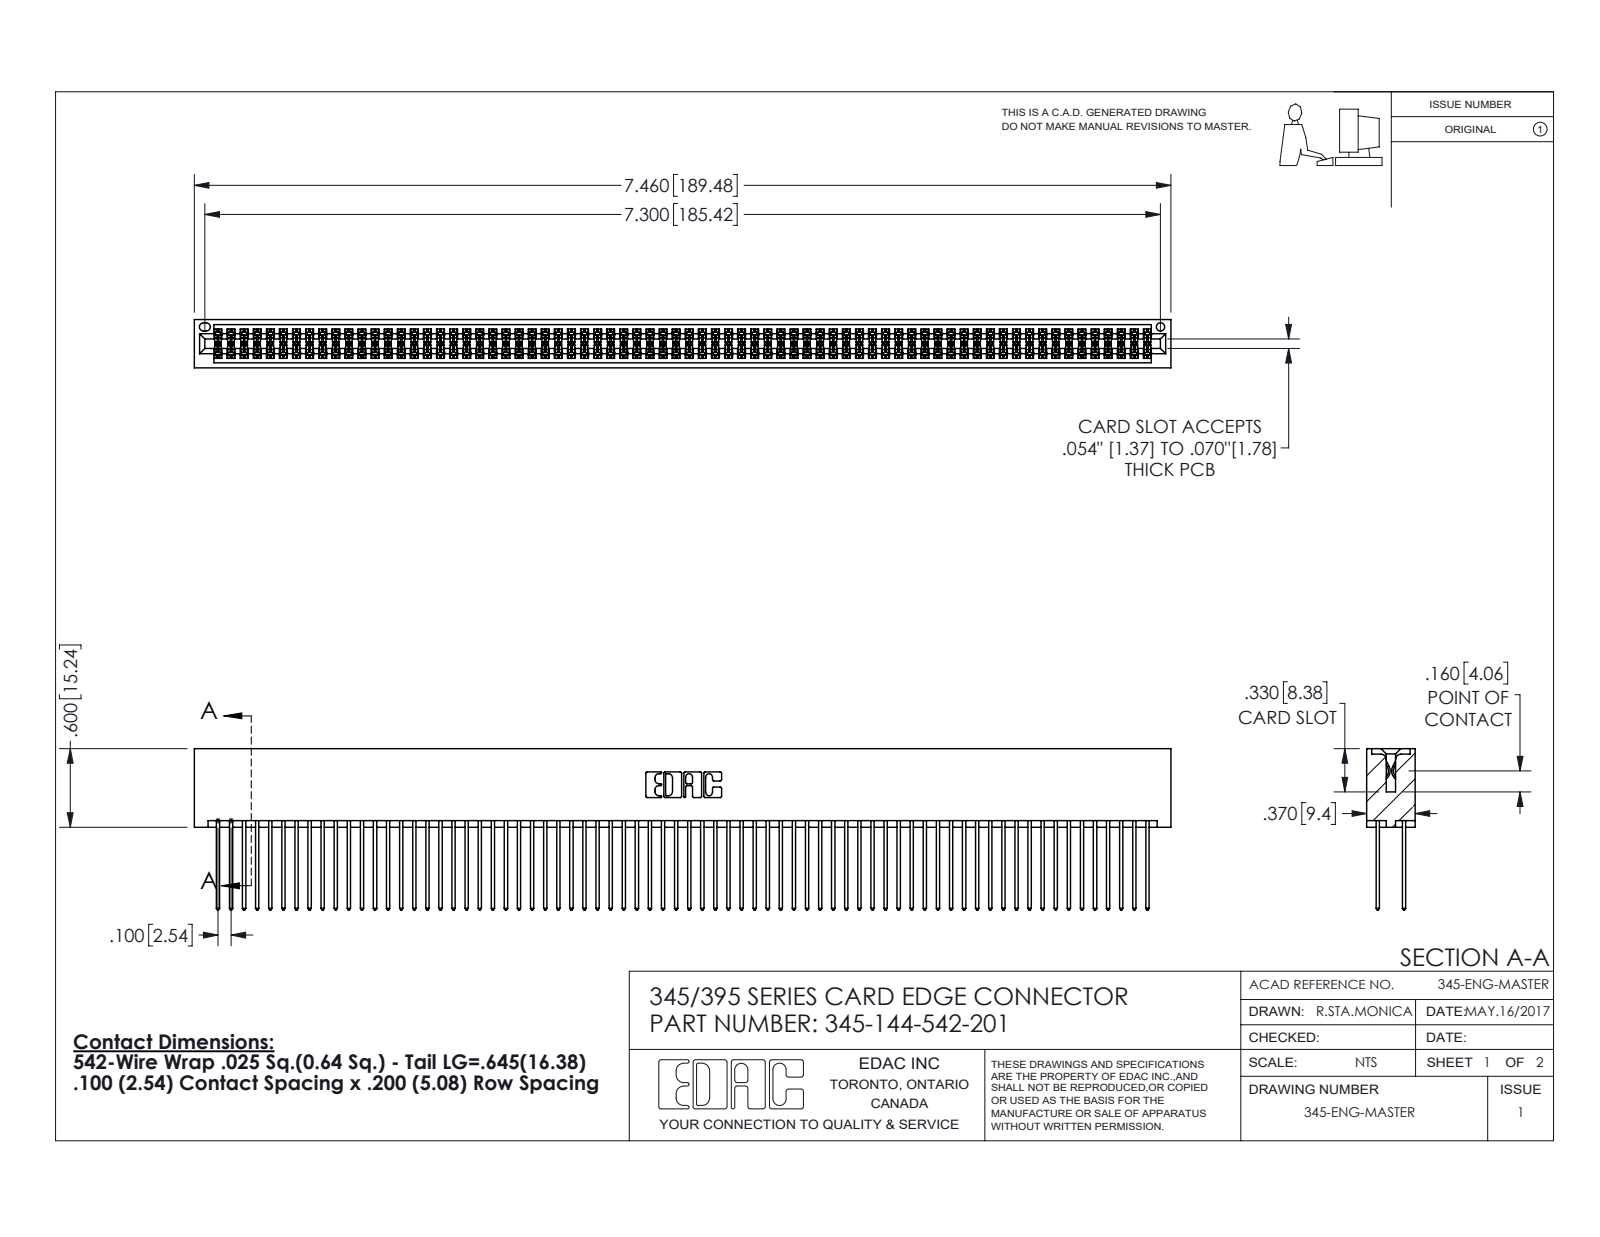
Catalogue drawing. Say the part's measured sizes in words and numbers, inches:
The part is named "345 Part_No Mounting Lugs; 345-292-001_345-293-142; 345-144-542-201". Its 3-D file was written by "SolidWorks 2016 (CONFIG_CONTROL_DESIGN)". It is 145 solids with 7318 faces: 4828 planar, 2490 cylindrical and 0 other. Overall it measures 7.46 by 1.232 by 0.37 inches. Its volume is 1.219 cubic inches and its surface area 51.99 square inches. Round holes: 1 of diameter 0.064. Partial cylindrical surfaces (rounded edges, fillets, slot ends): 216 of radius 0.006, 144 of radius 0.01, 22 of radius 0.01, 6 of radius 0.007, 6 of radius 0.031, 3 of radius 0.026, 2 of radius 0.014, 2 of radius 0.019. The main face-to-face distances are 0.298, 0.072, 0.2, 0.098, 0.272, 0.025, 0.225, 0.37, 0.175, 0.149.
